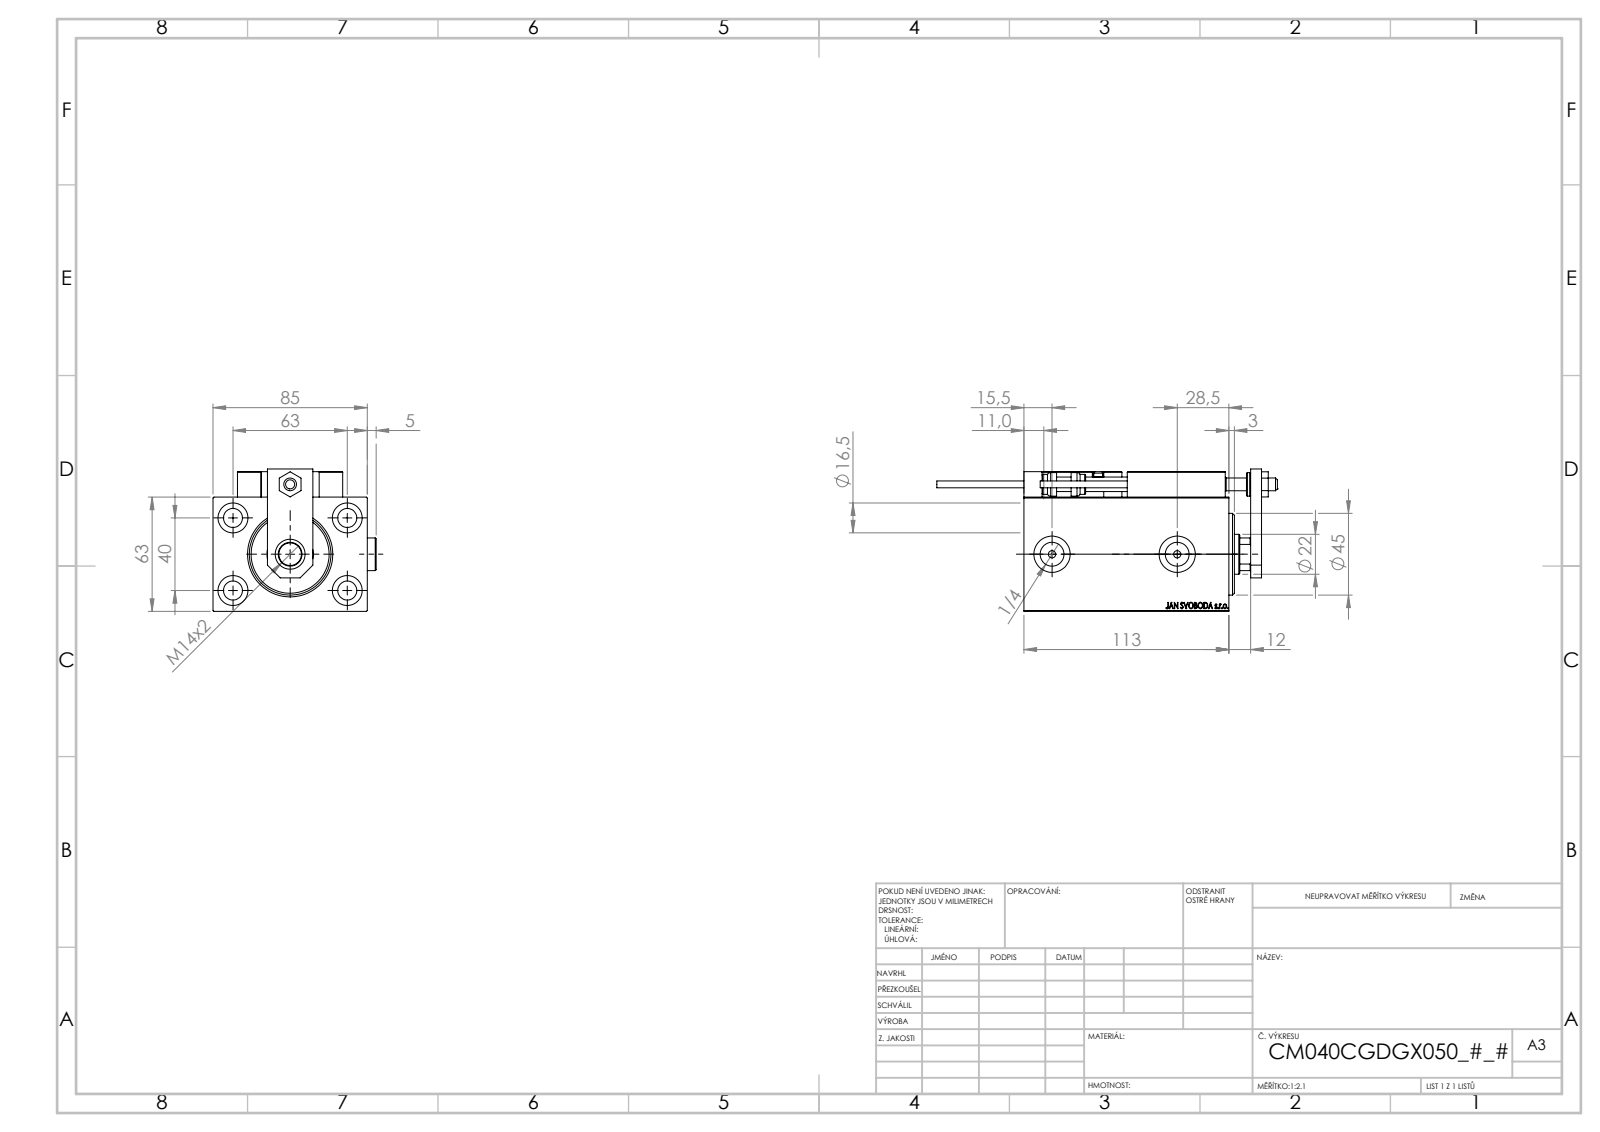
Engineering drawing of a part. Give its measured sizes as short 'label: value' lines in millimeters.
name: NUT_D12; V450CM_VC_B; Block; SWITCH X (+8 more)
written by: SolidWorks 2019 (CONFIG_CONTROL_DESIGN)
unit: mm
bodies: 25 solids, 1336 faces (594 planar, 204 cylindrical, 538 other)
size: 187.7 × 89.9 × 78.5
volume: 560 383 mm³; area: 120 963 mm²
holes: 6× ⌀4, 5× ⌀8, 5× ⌀16.5, 4× ⌀3.2, 4× ⌀10.5, 2× ⌀5, 2× ⌀13.16, 2× ⌀20, 1× ⌀7, 1× ⌀12.5, 1× ⌀22, 1× ⌀25.5
bosses: 2× ⌀18, 2× ⌀5, 2× ⌀3.8, 1× ⌀13, 1× ⌀11
rounds: 30× R0.3, 2× R3, 1× R10.5
face distances: 63, 85, 12, 101, 113, 14, 77, 3, 6, 15
hole spacings: 37.31, 11.37, 20, 29.59, 29.69, 36.06, 36.53, 40
